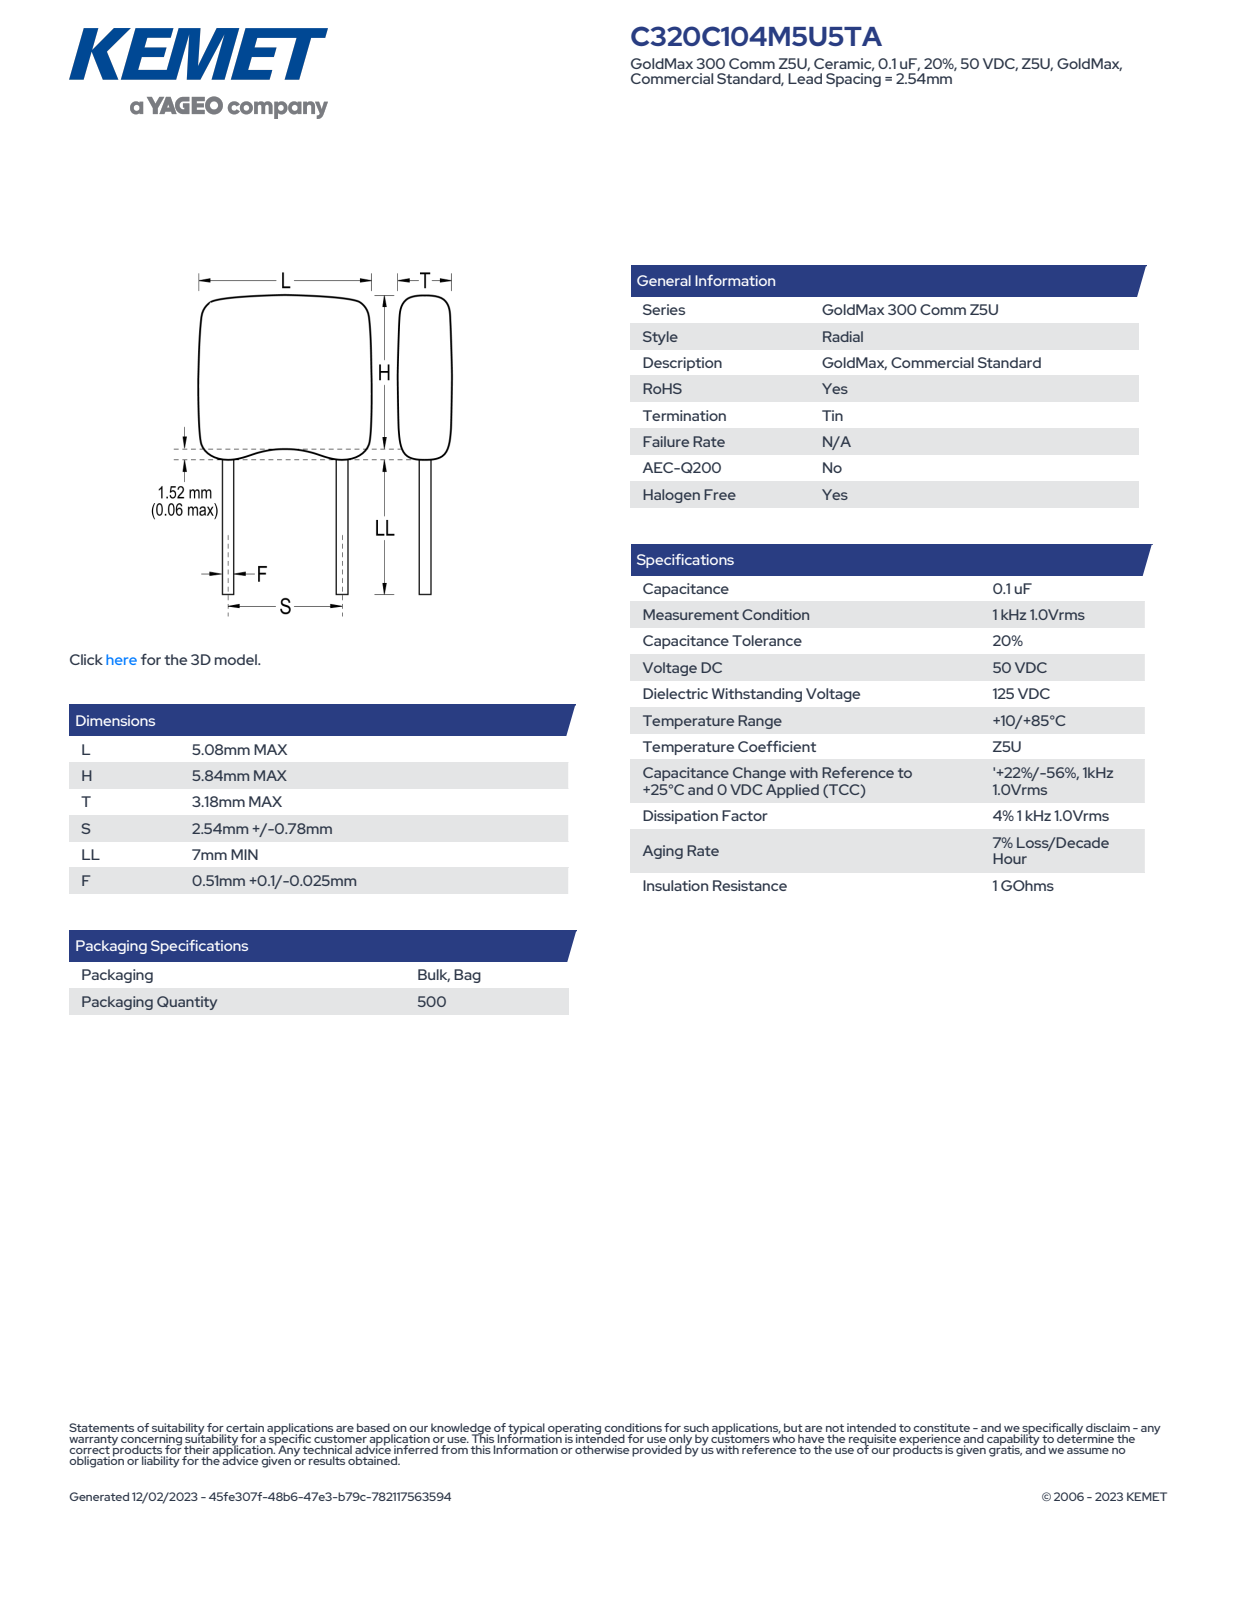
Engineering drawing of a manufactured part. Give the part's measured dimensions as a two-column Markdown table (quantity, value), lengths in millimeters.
| quantity | value |
| --- | --- |
| part name | CCR_KRCST_C320_L5.08H5.84T3.18S2.54LL7F0.61 |
| STEP written by | SolidWorks 2014 (AUTOMOTIVE_DESIGN) |
| units | millimeters |
| bodies | 4 solids, 83 faces (65 planar, 14 cylindrical, 4 other) |
| overall size | 14.36 × 5.08 × 3.19 |
| volume | 117 mm³ |
| surface area | 164 mm² |
| round bosses / shafts (diameter × count) | 0.61 × 2 |
| partial cylindrical surfaces (radius × count) | 0.75 × 10 |
| main face-to-face distances | 3.18, 5.08, 7.36, 7, 14.36, 3.19, 0.54, 10.98, 3.98, 3.38 |
